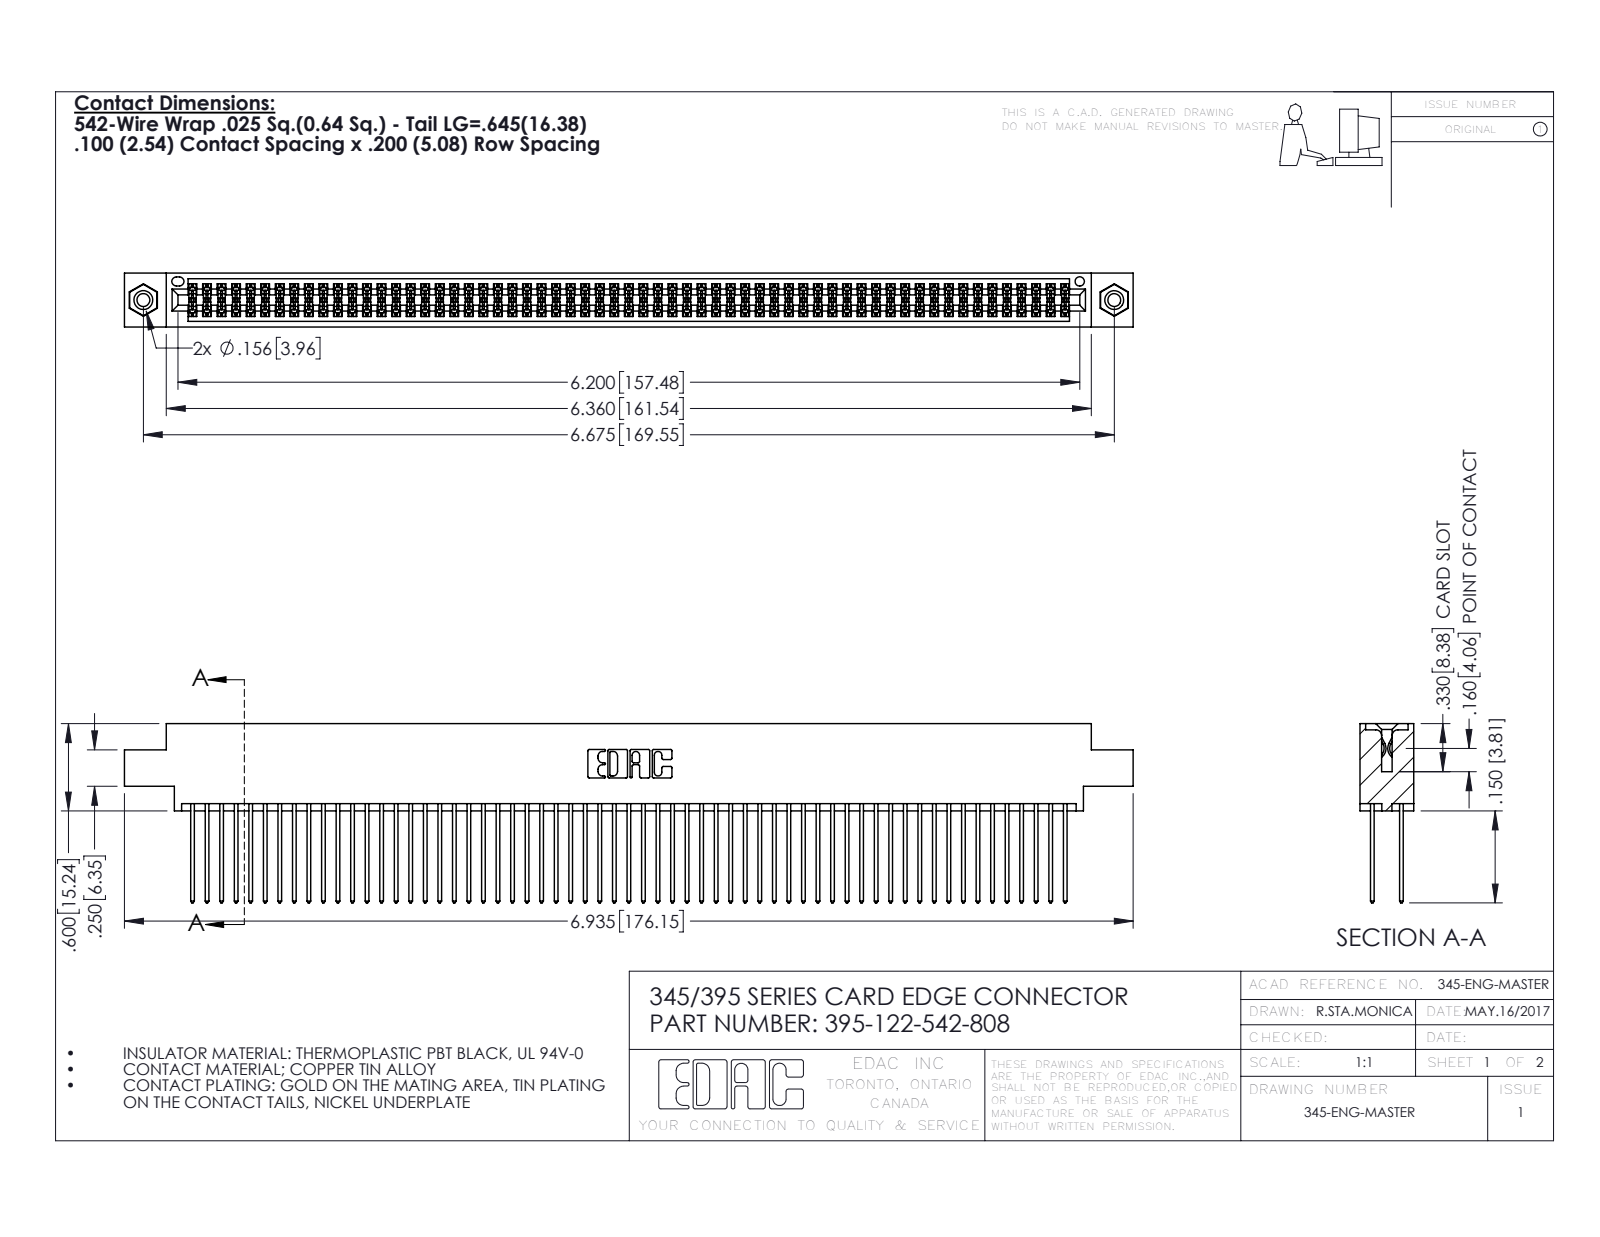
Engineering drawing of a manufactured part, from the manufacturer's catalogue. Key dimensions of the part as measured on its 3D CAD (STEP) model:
Part name (STEP PRODUCT): 345-250-001_345-250-003-102; 345 Part_0.170 Offset - 0.156 Dia-TI; 345-292-001_345-293-142; 395-122-542-808
STEP written by: SolidWorks 2016 (CONFIG_CONTROL_DESIGN)
Units: inches
Bodies: 125 solids, 6290 faces (4142 planar, 2132 cylindrical, 16 other)
Overall size (bounding box): 6.935 × 1.232 × 0.37
Volume: 1.082 in³ · Surface area: 45.57 in²
Round holes (diameter × count): ⌀0.089 ×2, ⌀0.125 ×2, ⌀0.156 ×2, ⌀0.064 ×1
Round bosses / shafts (diameter × count): ⌀0.155 ×2
Partial cylindrical surfaces — rounded edges, fillets, slot ends (radius × count): R0.006 ×183, R0.01 ×122, R0.01 ×22, R0.007 ×6, R0.031 ×6, R0.026 ×3, R0.014 ×2, R0.019 ×2
Main face-to-face distances: 0.072, 0.298, 0.2, 0.098, 0.272, 0.025, 0.37, 0.225, 0.175, 0.149
Hole centre spacings: 0.27, 6.439, 6.675
